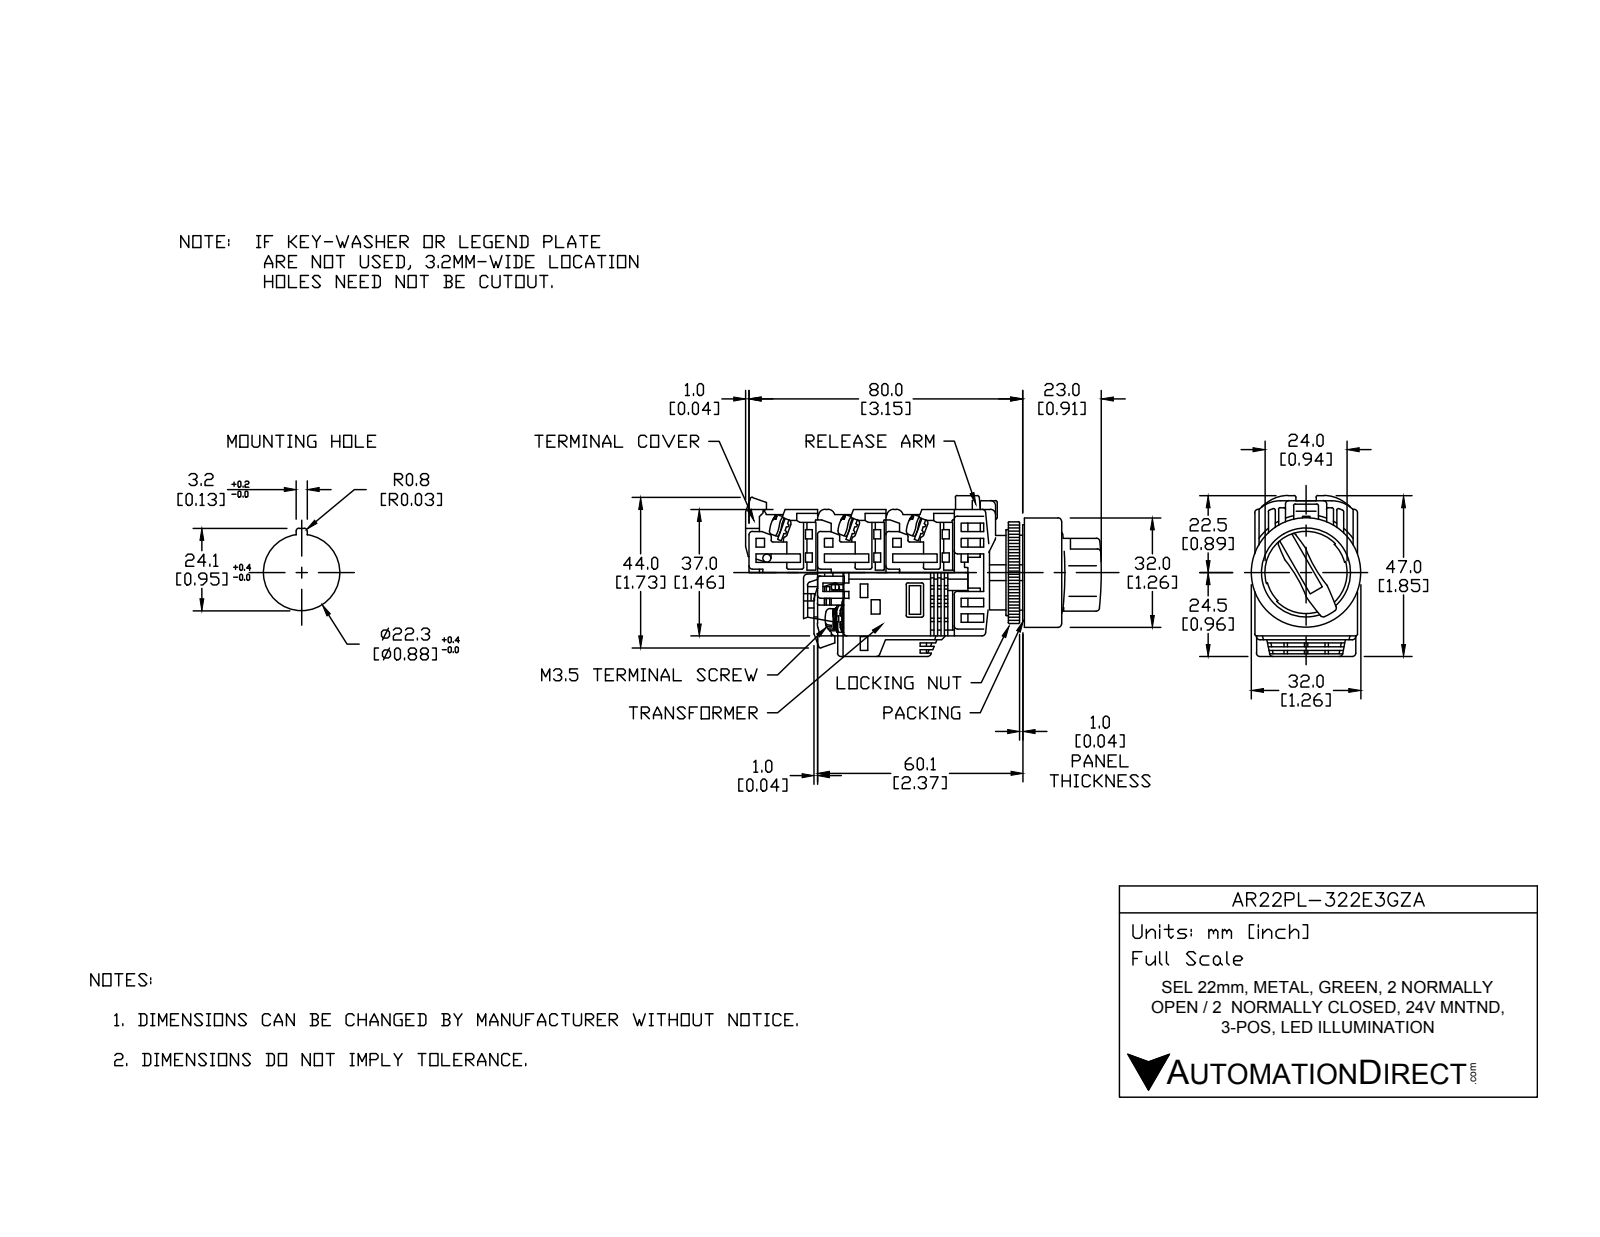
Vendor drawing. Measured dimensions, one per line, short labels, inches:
name: AR22PL-322E3GZA
written by: SolidWorks 2017 (AUTOMOTIVE_DESIGN)
unit: in
bodies: 33 solids, 744 faces (524 planar, 181 cylindrical, 39 other)
size: 4.114 × 1.725 × 1.26
volume: 3.913 in³; area: 54.8 in²
holes: 1× ⌀0.858, 1× ⌀0.866, 1× ⌀0.984, 1× ⌀1.22
bosses: 10× ⌀0.197, 1× ⌀1.26, 1× ⌀1.201, 1× ⌀1.173, 1× ⌀0.945, 1× ⌀0.856, 1× ⌀0.669
rounds: 66× R0.02, 8× R0.069, 6× R0.039, 4× R0.197, 2× R0.157, 1× R0.472, 1× R0.653, 1× R0.693
face distances: 0.787, 0.039, 0.709, 1.575, 1.142, 0.118, 0.354, 0.394, 0.079, 0.748
